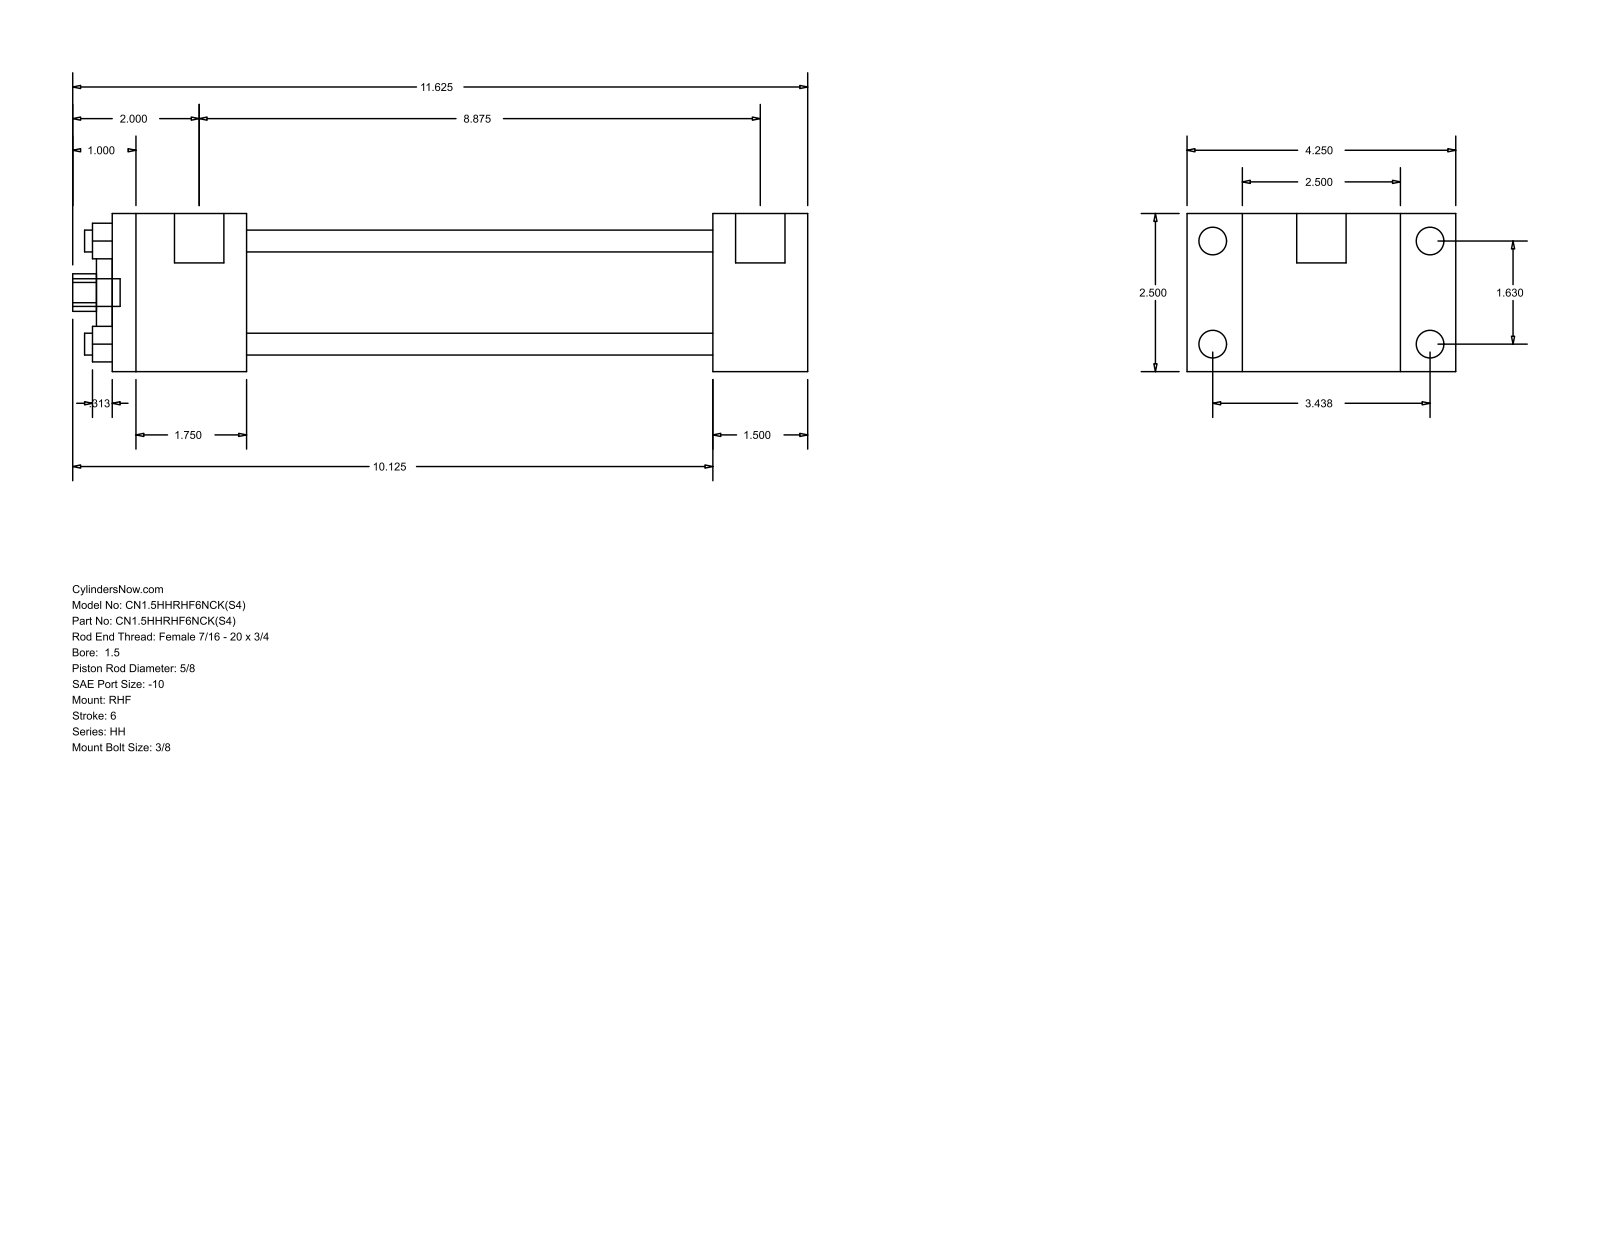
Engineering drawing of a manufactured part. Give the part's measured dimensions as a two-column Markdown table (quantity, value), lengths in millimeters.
| quantity | value |
| --- | --- |
| part name | HH_RHF__0150_0.625 |
| STEP written by | GSSL Pune (CONFIG_CONTROL_DESIGN) |
| units | millimeters |
| bodies | 0 solids, 88 faces (60 planar, 28 cylindrical, 0 other) |
| overall size | 295.27 × 107.95 × 63.5 |
| round holes (diameter × count) | 8.76 × 4, 15.88 × 1, 28.57 × 1, 44.45 × 1 |
| round bosses / shafts (diameter × count) | 11.13 × 4, 5.56 × 4, 19.84 × 2, 11.11 × 1 |
| partial cylindrical surfaces (radius × count) | 7.54 × 1 |
| main face-to-face distances | 63.5, 22.23, 85.73, 38.09, 241.3, 279.39, 107.96, 53.97, 187.33, 225.42 |
| hole center spacings | 29.27, 41.4, 58.55 |
